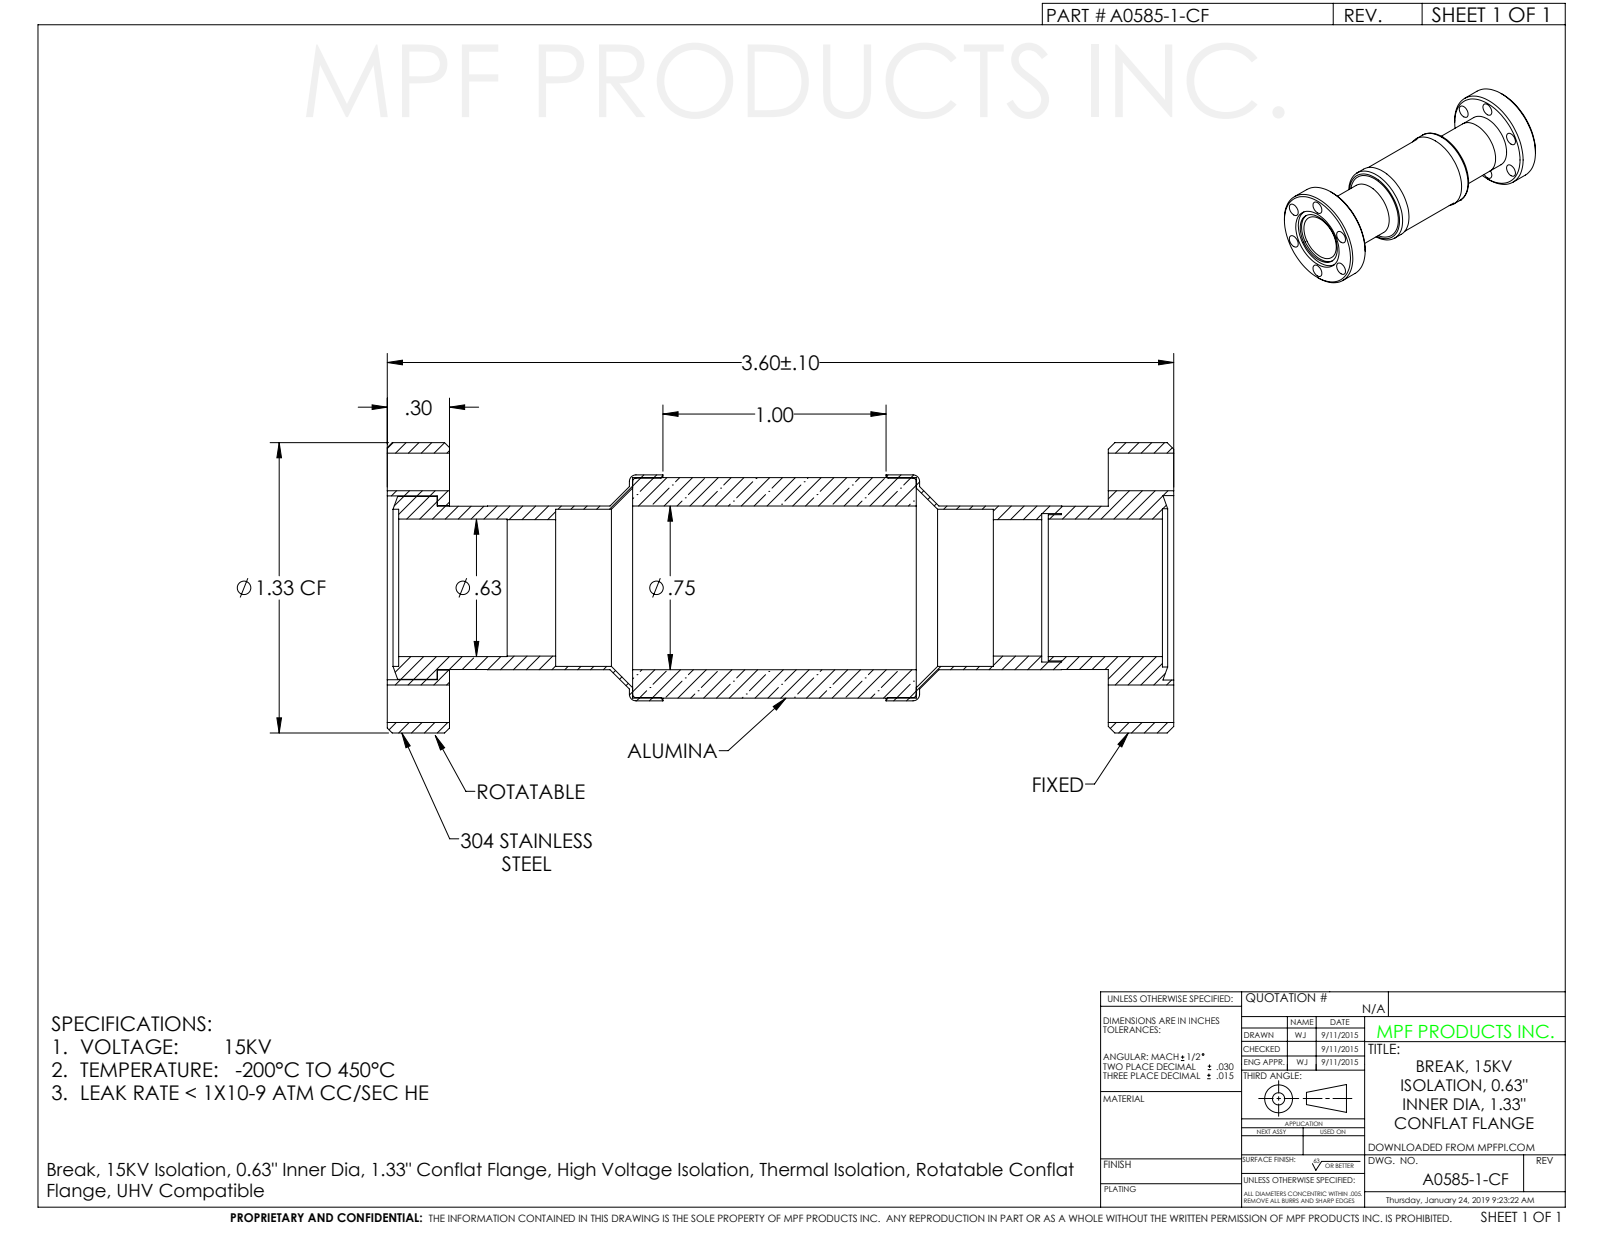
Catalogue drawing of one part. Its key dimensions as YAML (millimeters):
part_name: "A0585-1-CF"
step_written_by: "SolidWorks 2019 (CONFIG_CONTROL_DESIGN)"
units: millimeters
bodies: {solids: 1, faces: 114, planar: 22, cylindrical: 72, other: 20}
overall_size: [92.2, 33.8, 33.8]
volume: 19600
surface_area: 16460
round_holes:
  - {diameter: 4.4, count: 12}
  - {diameter: 15.9, count: 1}
  - {diameter: 16, count: 1}
  - {diameter: 17.3, count: 1}
  - {diameter: 18.3, count: 1}
  - {diameter: 18.4, count: 1}
  - {diameter: 21.5, count: 1}
  - {diameter: 21.5, count: 1}
round_bosses_or_shafts:
  - {diameter: 33.8, count: 1}
  - {diameter: 26.3, count: 1}
  - {diameter: 25.4, count: 1}
  - {diameter: 19.1, count: 1}
  - {diameter: 19, count: 1}
  - {diameter: 17, count: 1}
face_to_face_distances: [7.6, 84.6, 77, 92.2, 1.3, 90.9, 6.3, 83.3, 20.6, 71.6]
hole_center_spacings: [13.5, 23.4, 6.2, 13.5, 26.2, 7.7, 18.5, 25.9]
